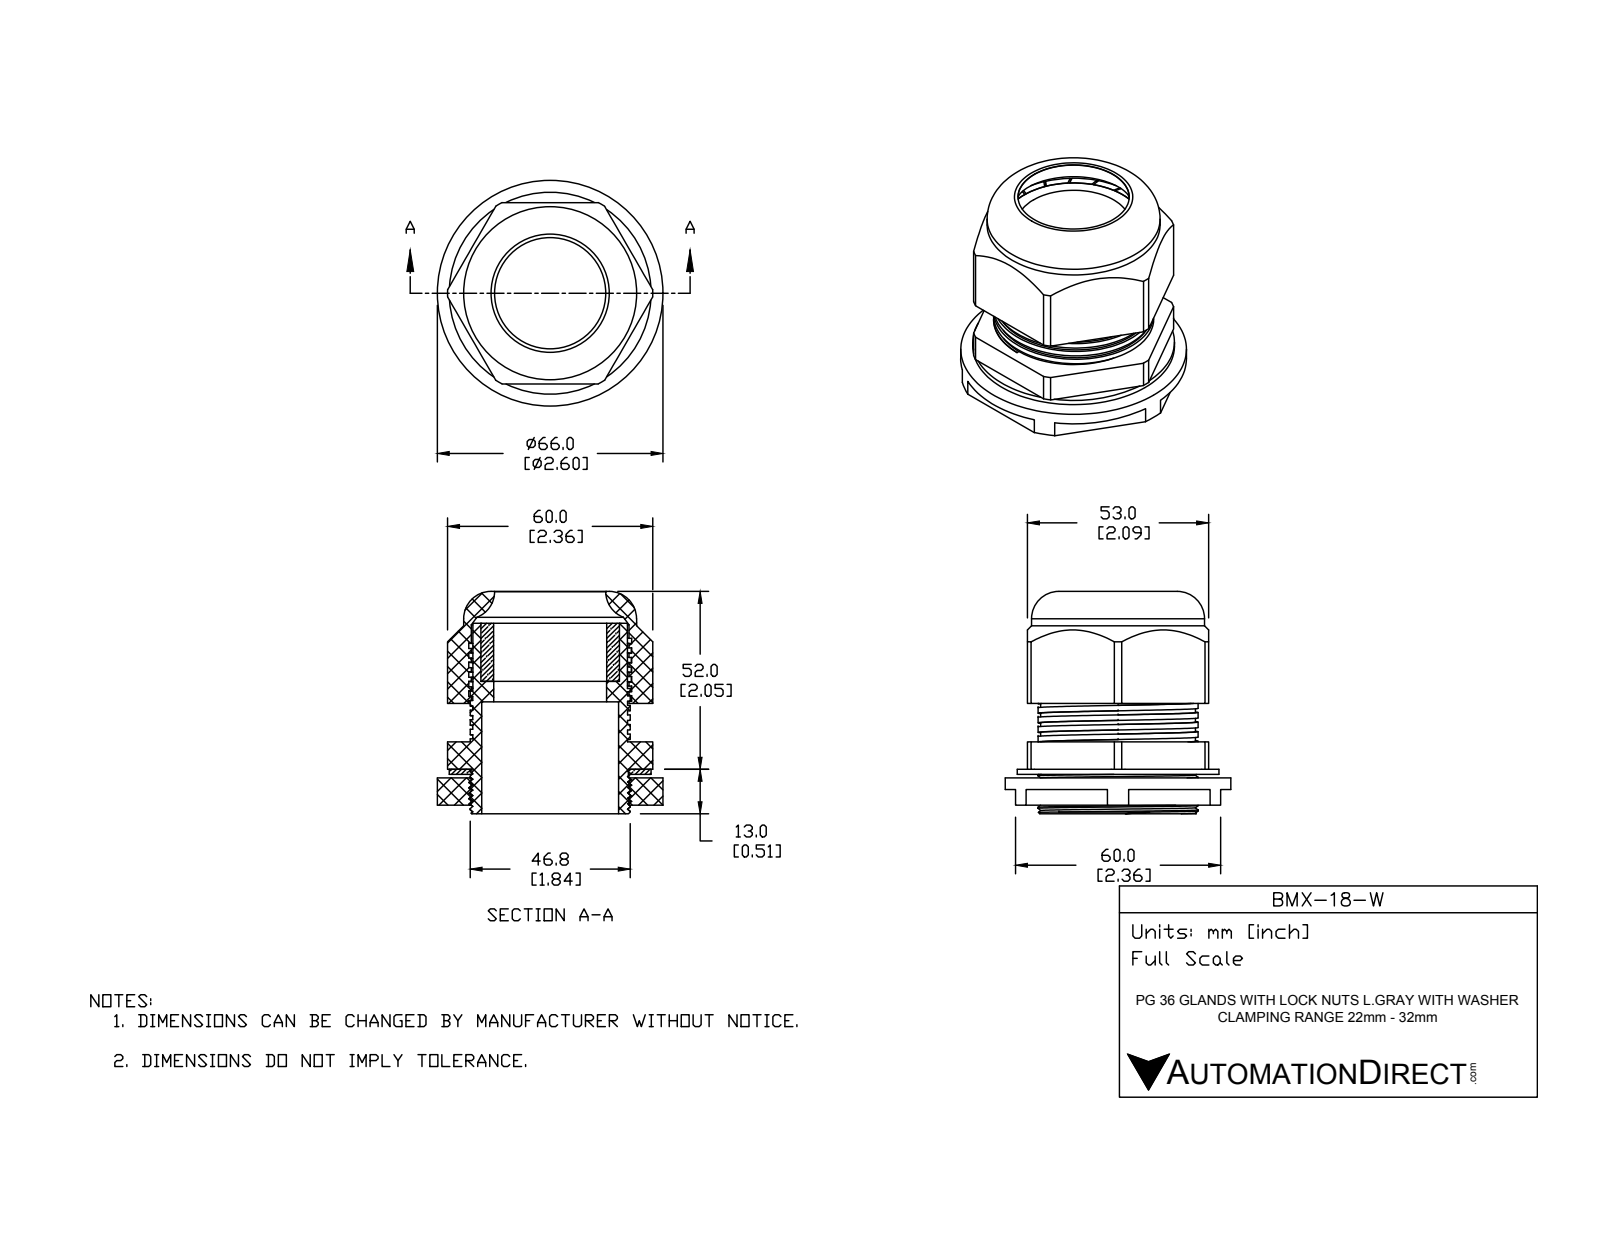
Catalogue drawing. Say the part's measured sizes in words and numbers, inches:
The part is named "BMX-18-W". Its 3-D file was written by "SolidWorks 2015 (CONFIG_CONTROL_DESIGN)". It is 5 solids with 223 faces: 111 planar, 91 cylindrical and 21 other. Overall it measures 2.598 by 2.598 by 2.559 inches. Its volume is 4.434 cubic inches and its surface area 76.33 square inches. Round holes: 1 of diameter 1.28, 1 of diameter 1.299, 1 of diameter 1.303, 1 of diameter 1.575, 1 of diameter 1.594, 1 of diameter 1.803, 1 of diameter 1.816. Round bosses or shafts: 1 of diameter 2.598, 1 of diameter 2.323, 1 of diameter 1.992, 1 of diameter 1.843, 1 of diameter 1.78. Partial cylindrical surfaces (rounded edges, fillets, slot ends): 1 of radius 1.181. The main face-to-face distances are 0.413, 2.087, 0.315, 0.098, 0.354, 0.039, 0.059, 1.425, 1.11, 1.071.
